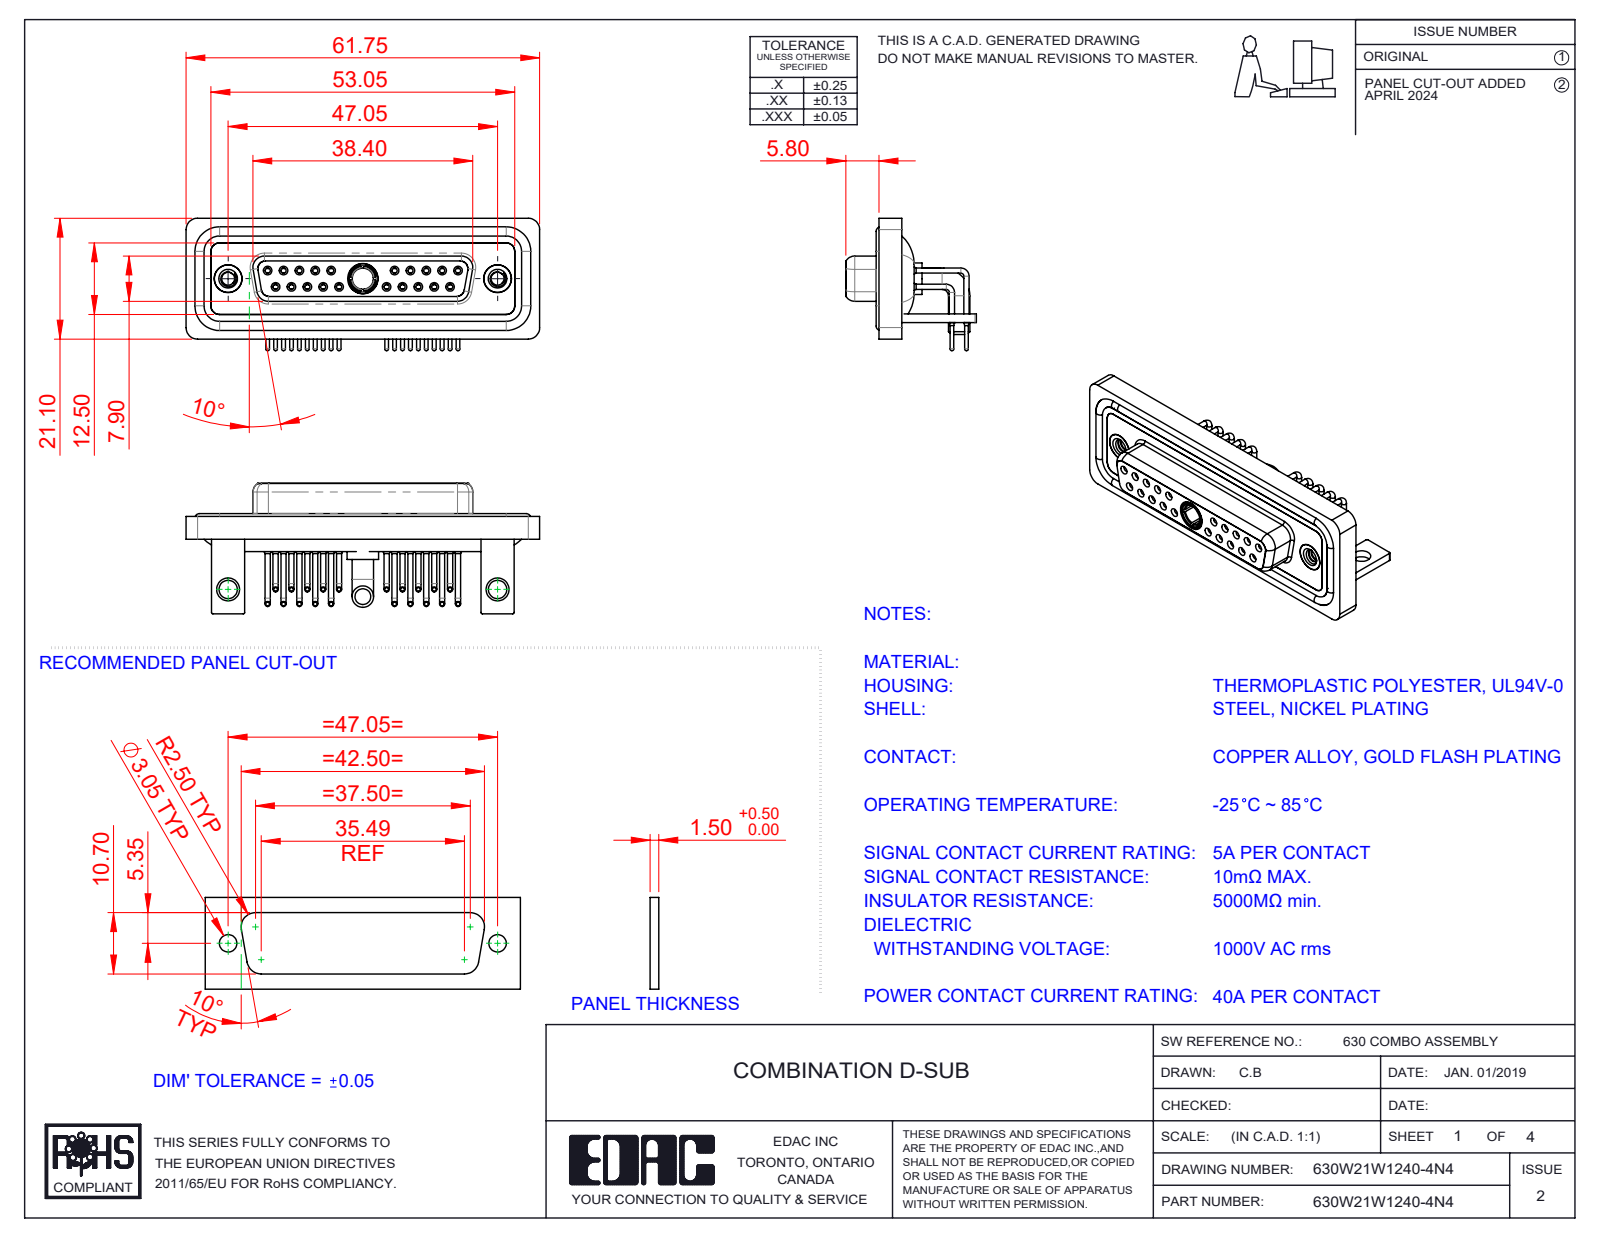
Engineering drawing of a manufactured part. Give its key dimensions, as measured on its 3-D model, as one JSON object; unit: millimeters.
{"part_name": "630Combo Waterproof Housing_25 Contacts; 630Combo Contact Row 1_50 Contacts; 630Combo Shell Rear_25 Contacts; 630Combo Contact Row 2_50 Contacts (+6 more)", "step_written_by": "SolidWorks 2023 (CONFIG_CONTROL_DESIGN)", "units": "millimeters", "bodies": {"solids": 31, "faces": 1572, "planar": 454, "cylindrical": 697, "other": 421}, "overall_size": [61.75, 23.12, 22.8], "volume_mm3": 8945, "surface_area_mm2": 15559, "round_holes": [[0.9, 20], [1.1, 20], [1.5, 20], [2, 20], [1.6, 10], [1.7, 10], [4.85, 3], [2.26, 2], [3.2, 2], [4, 2], [4.05, 2], [5, 2]], "round_bosses_or_shafts": [[0.9, 20], [0.65, 20], [1.6, 14], [4.95, 2], [4.8, 2], [3.75, 2], [5.5, 1], [5.2, 1]], "partial_cylinders_radius": [[2, 19], [1.5, 18], [0.25, 16], [1.35, 8], [1.6, 8], [0.5, 5], [0.6, 4], [0.65, 4]], "face_to_face_distances": [0.4, 1.8, 2.9, 3.7, 1.5, 4.1, 1.1, 1.4, 1.6, 2.5], "hole_center_spacings": [3.16, 2.77, 5.54, 8.31, 5.04, 19.39, 20.97, 22.16]}
